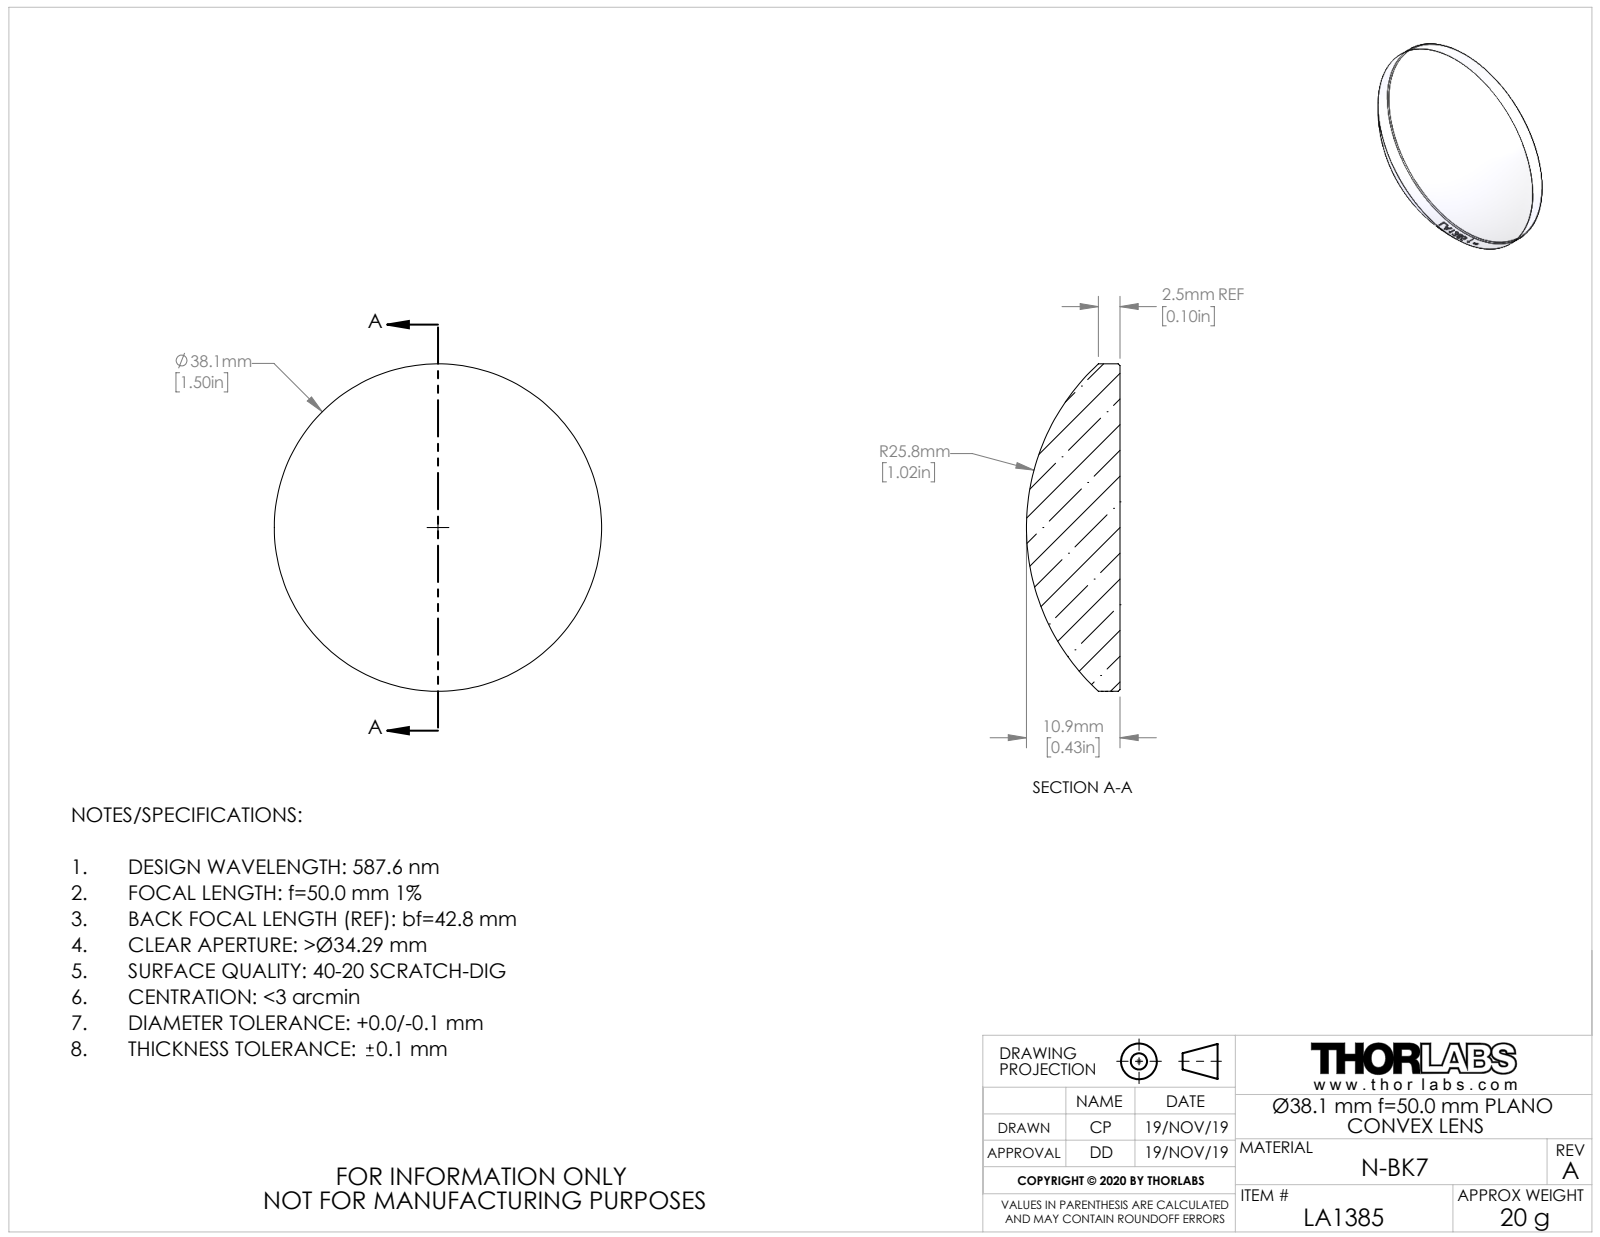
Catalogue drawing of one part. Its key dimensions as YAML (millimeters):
part_name: "TTN200652-E0W"
step_written_by: "SolidWorks 2018 (CONFIG_CONTROL_DESIGN)"
units: millimeters
bodies: {solids: 1, faces: 20, planar: 1, cylindrical: 15, other: 4}
overall_size: [38.1, 38.1, 10.88]
volume: 7932
surface_area: 2786
round_bosses_or_shafts:
  - {diameter: 38.1, count: 1}
